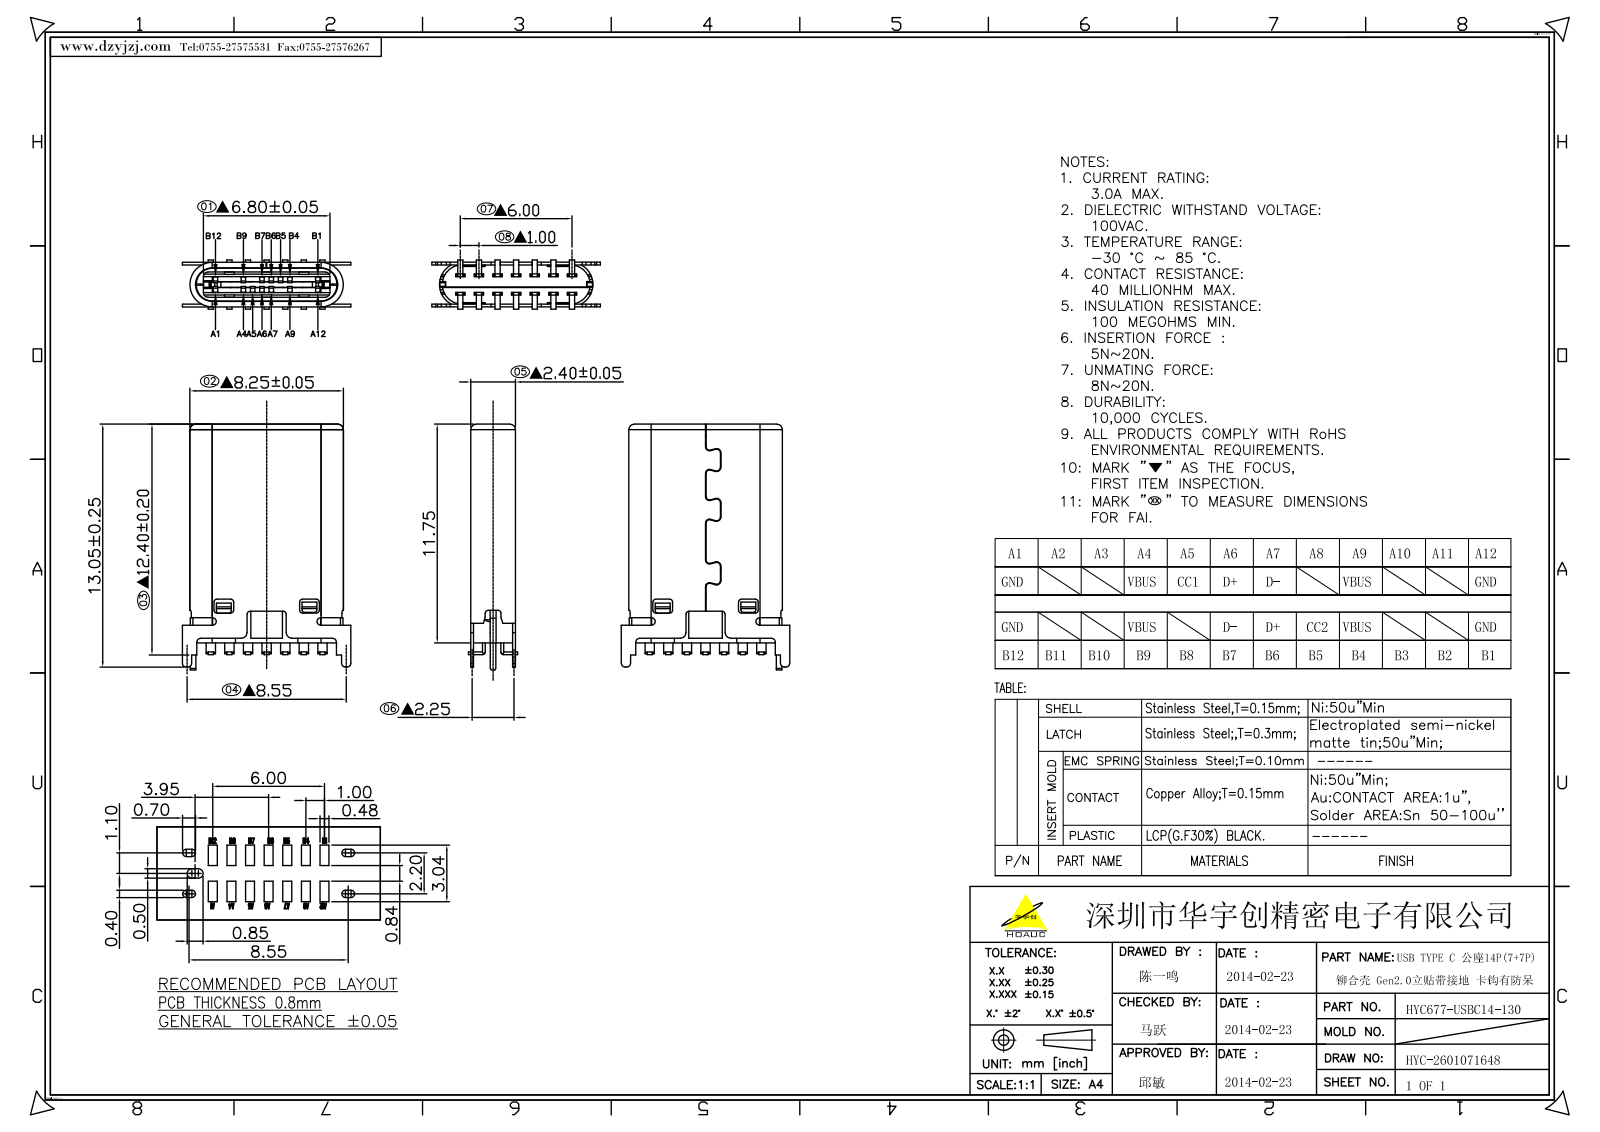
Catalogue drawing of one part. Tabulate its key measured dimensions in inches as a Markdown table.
| quantity | value |
| --- | --- |
| part name | TANPIAN-PLASTIC_1_2__2_1__1_1_1 |
| STEP written by | CREO PARAMETRIC BY PTC INC, 2022073 (CONFIG_CONTROL_DESIGN) |
| units | inches |
| bodies | 1 solid, 759 faces (577 planar, 178 cylindrical, 4 other) |
| overall size | 0.52 × 0.356 × 0.104 |
| volume | 0.011 in³ |
| surface area | 0.657 in² |
| partial cylindrical surfaces (radius × count) | 0.006 × 30, 0.008 × 22, 0.005 × 10, 0.012 × 8, 0.007 × 6, 0.009 × 6, 0.01 × 6, 0.004 × 4 |
| main face-to-face distances | 0.094, 0.03, 0.064, 0.034, 0.044, 0.02, 0.074, 0.015, 0.068, 0.089 |
